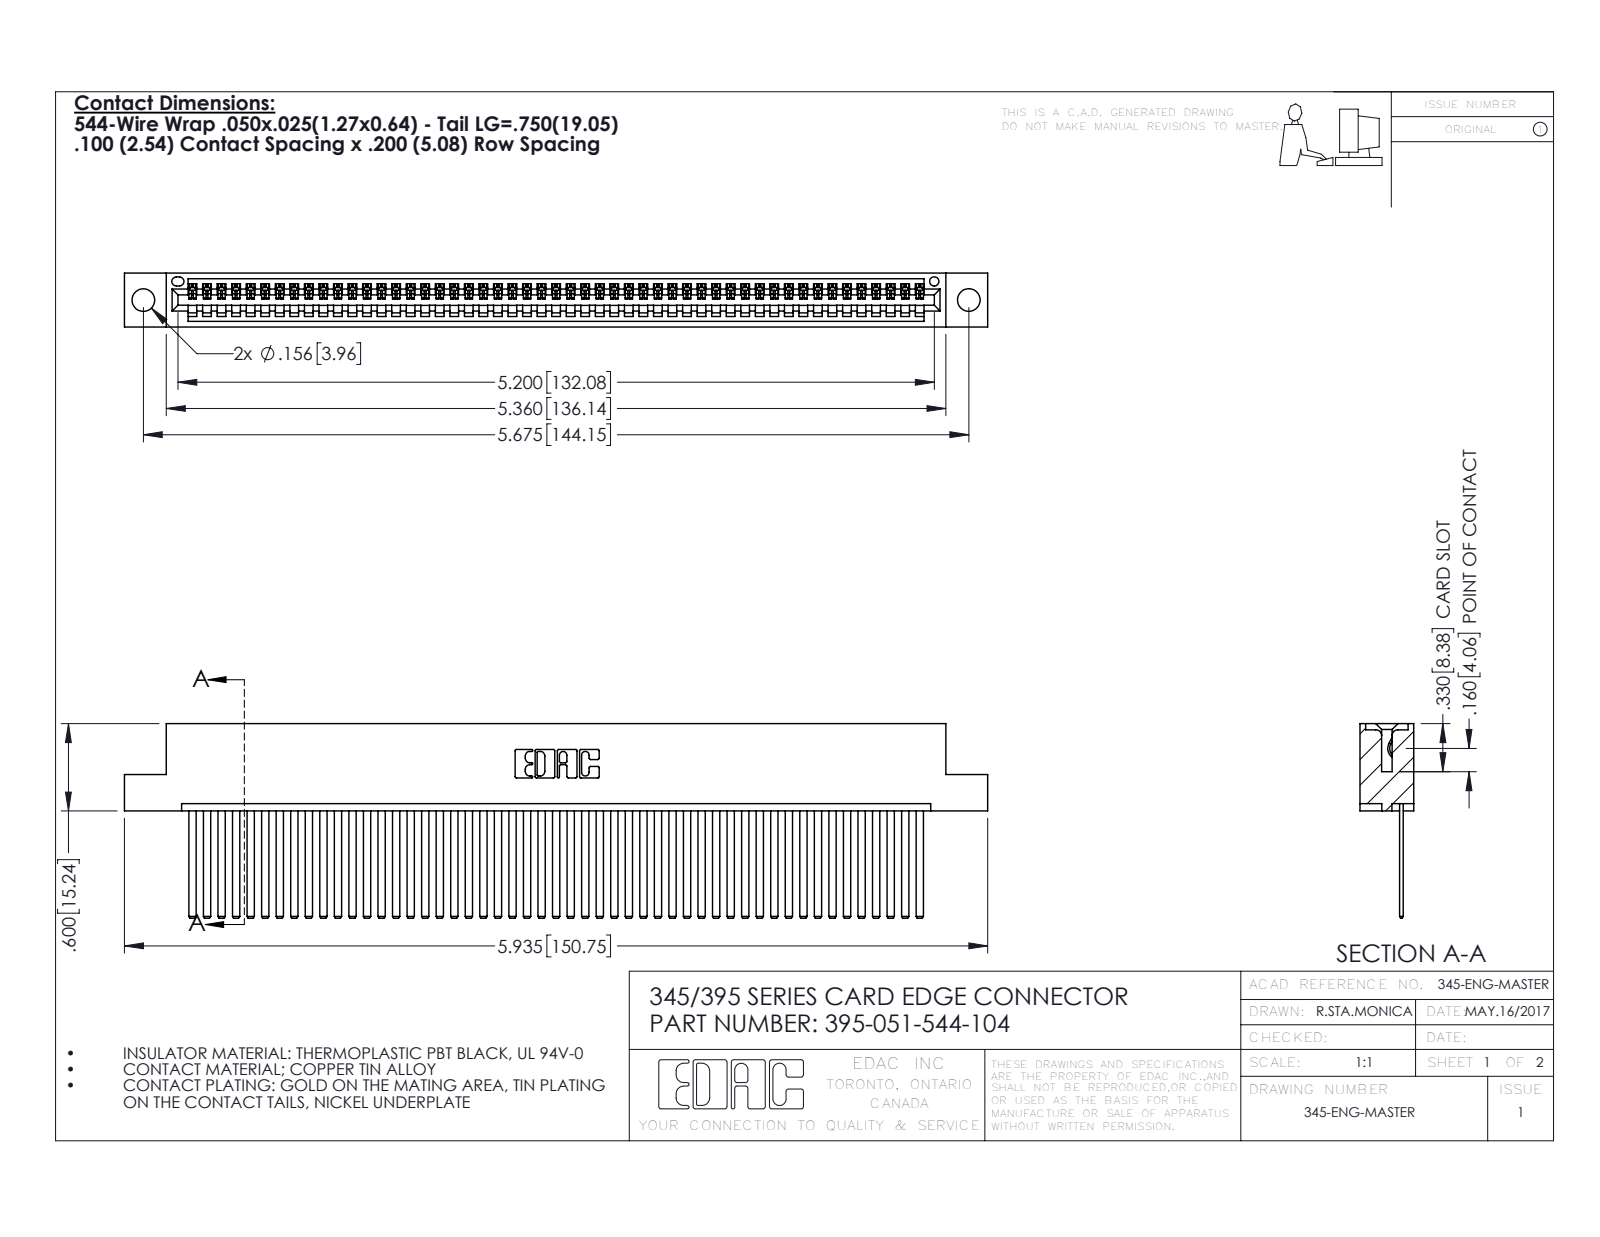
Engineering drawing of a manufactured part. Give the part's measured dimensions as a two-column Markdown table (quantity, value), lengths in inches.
| quantity | value |
| --- | --- |
| part name | 345 Part_Flush Mounting Lugs - 0.156 Dia-TH; 345-292-001_345-293-144; 395-051-544-104 |
| STEP written by | SolidWorks 2016 (CONFIG_CONTROL_DESIGN) |
| units | inches |
| bodies | 52 solids, 2778 faces (1916 planar, 862 cylindrical, 0 other) |
| overall size | 5.935 × 1.337 × 0.37 |
| volume | 0.909 in³ |
| surface area | 33.32 in² |
| round holes (diameter × count) | 0.156 × 2, 0.064 × 1 |
| partial cylindrical surfaces (radius × count) | 0.006 × 102, 0.01 × 22, 0.007 × 6, 0.031 × 6, 0.026 × 3, 0.031 × 2, 0.04 × 2, 0.014 × 1 |
| main face-to-face distances | 0.072, 0.298, 0.025, 0.098, 0.272, 0.37, 0.2, 0.225, 0.149, 0.072 |
| hole center spacings | 0.27, 5.439, 5.675 |
